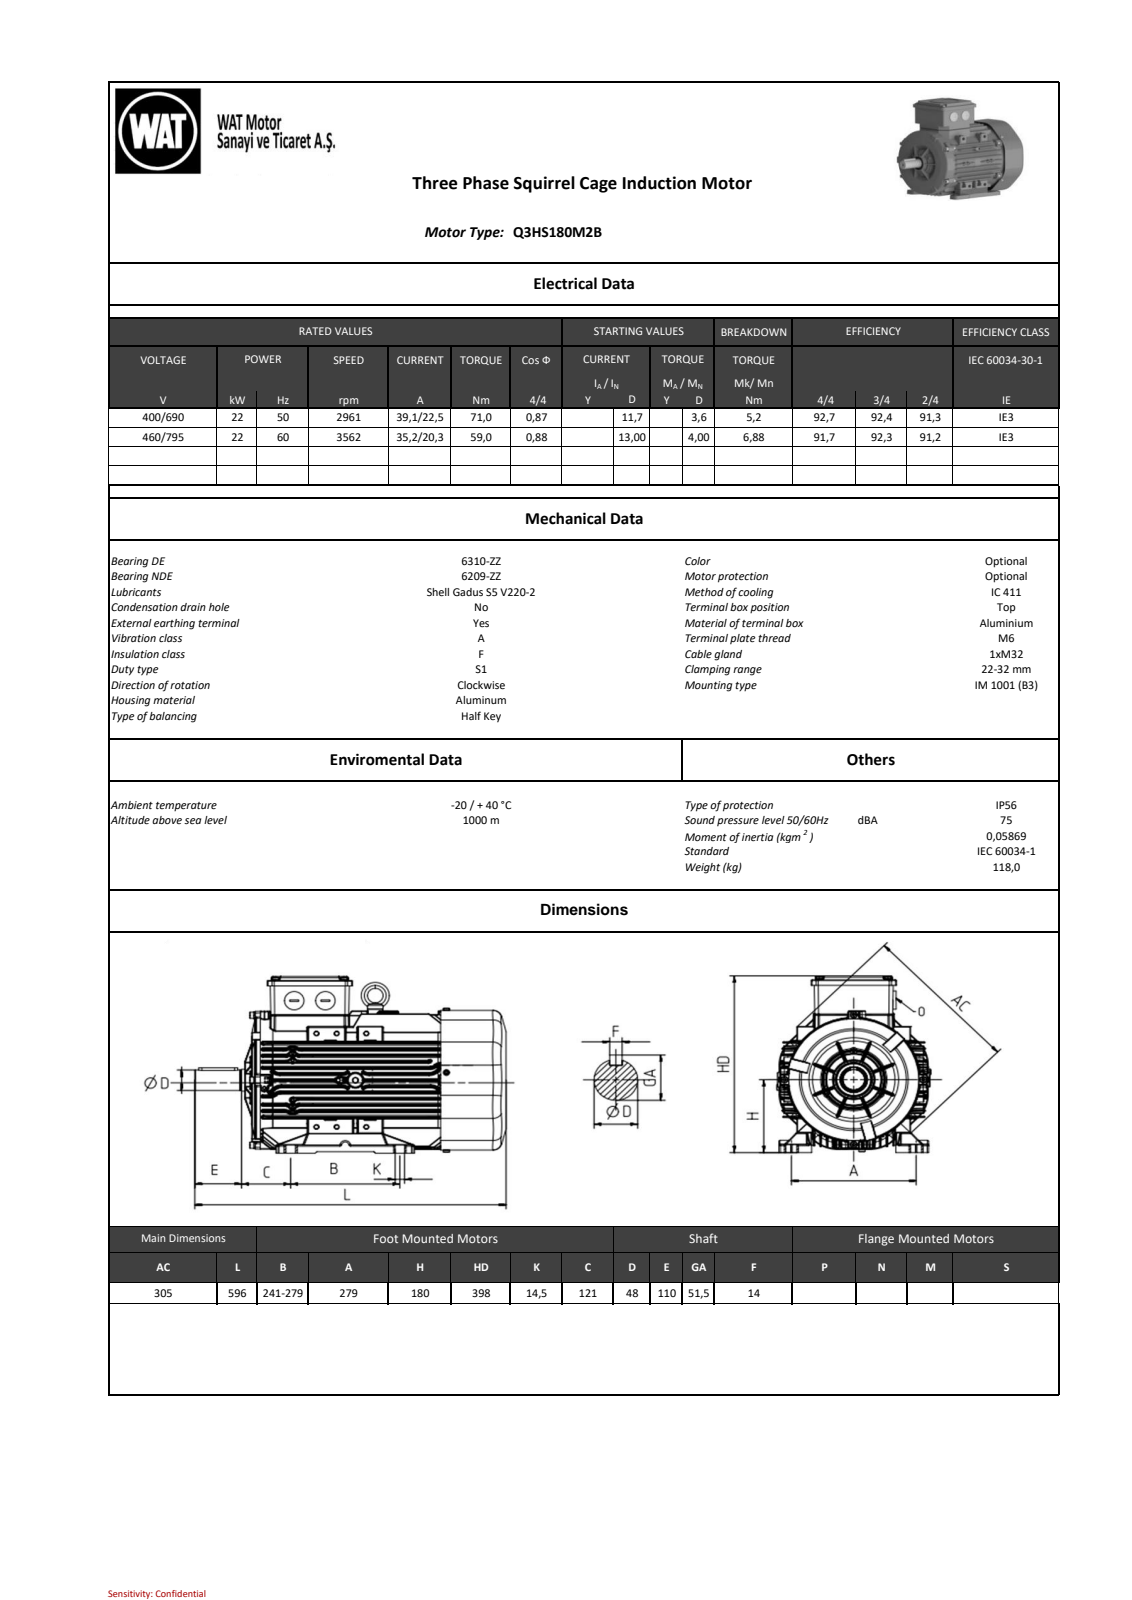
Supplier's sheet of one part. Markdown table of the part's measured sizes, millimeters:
| quantity | value |
| --- | --- |
| part name | 001_objects |
| STEP written by | SIEMENS PLM Software NX2206.8101 (AP203_CONFIGURATION_CONTROLLED_3D_DESIGN_OF_MECHANICAL_PARTS_AND_ASSEMBLIES_MIM_LF) |
| units | millimeters |
| bodies | 0 solids, 7946 faces (1826 planar, 3412 cylindrical, 2708 other) |
| overall size | 595.97 × 398.75 × 327.87 |
| round holes (diameter × count) | 6 × 4, 10 × 1, 17 × 1, 34.2 × 1, 52.5 × 1, 80 × 1, 85.63 × 1, 94 × 1, 114 × 1, 134 × 1, 154 × 1, 174 × 1 |
| round bosses / shafts (diameter × count) | 8 × 4, 38 × 2, 272.5 × 1, 178 × 1, 168 × 1, 158 × 1, 138 × 1, 118 × 1 |
| partial cylindrical surfaces (radius × count) | 0.5 × 724, 1 × 540, 2 × 357, 4 × 98, 2.5 × 66, 5 × 58, 3 × 29, 95.6 × 15 |
| main face-to-face distances | 144, 11.85, 165.47, 168, 9.32, 2.53, 156.15, 11.92, 1.5, 21.47 |
| hole center spacings | 59.75, 84.5, 59.51, 59.68, 59.83, 59.99, 119.5, 59.5 |
